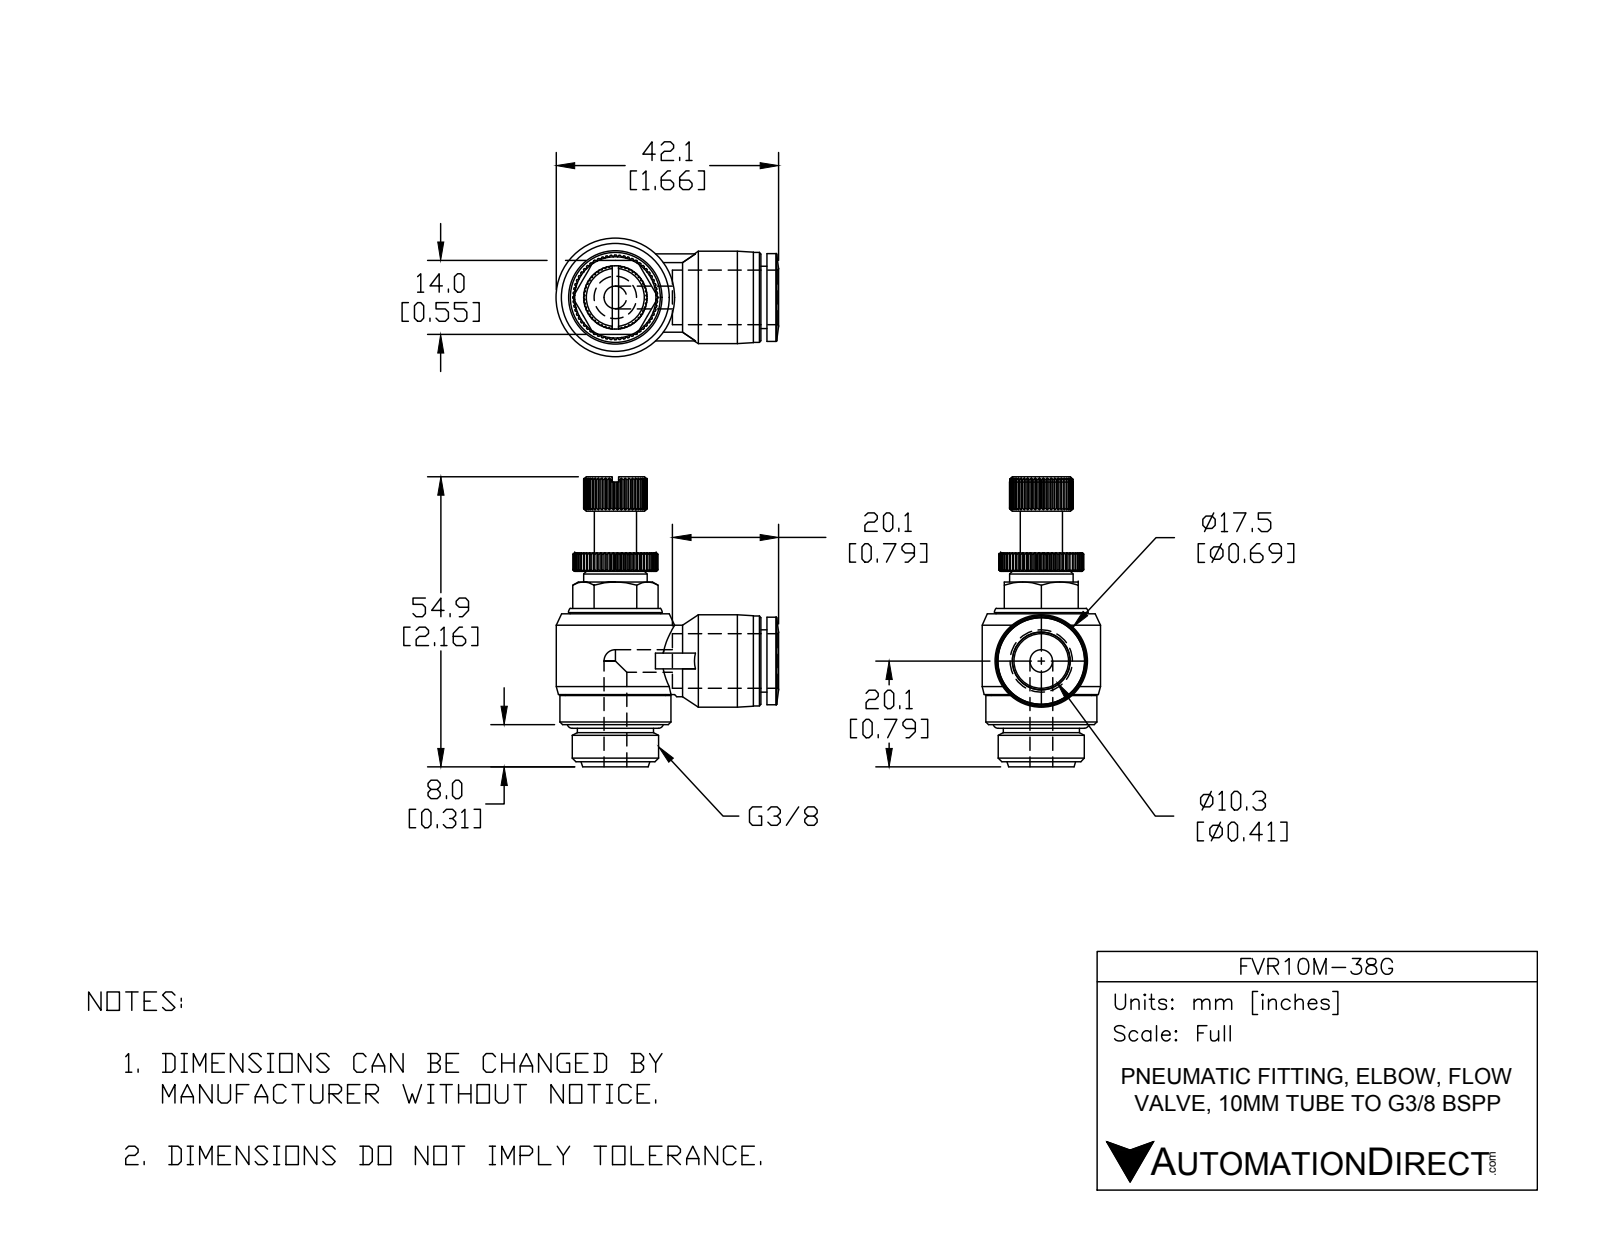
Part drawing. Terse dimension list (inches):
name: FVR10M-38G
written by: SolidWorks 2015 (AUTOMOTIVE_DESIGN)
unit: in
bodies: 2 solids, 571 faces (252 planar, 143 cylindrical, 176 other)
size: 2.161 × 1.657 × 0.882
volume: 0.896 in³; area: 10.66 in²
holes: 2× ⌀0.169, 1× ⌀0.406
bosses: 1× ⌀0.882, 1× ⌀0.827, 1× ⌀0.748, 1× ⌀0.689, 1× ⌀0.675, 1× ⌀0.669, 1× ⌀0.654, 1× ⌀0.642
rounds: 1× R0.315
face distances: 1.142, 0.705, 0.315, 0.551, 0.039, 1.594, 0.045, 1.063, 0.453, 0.276
